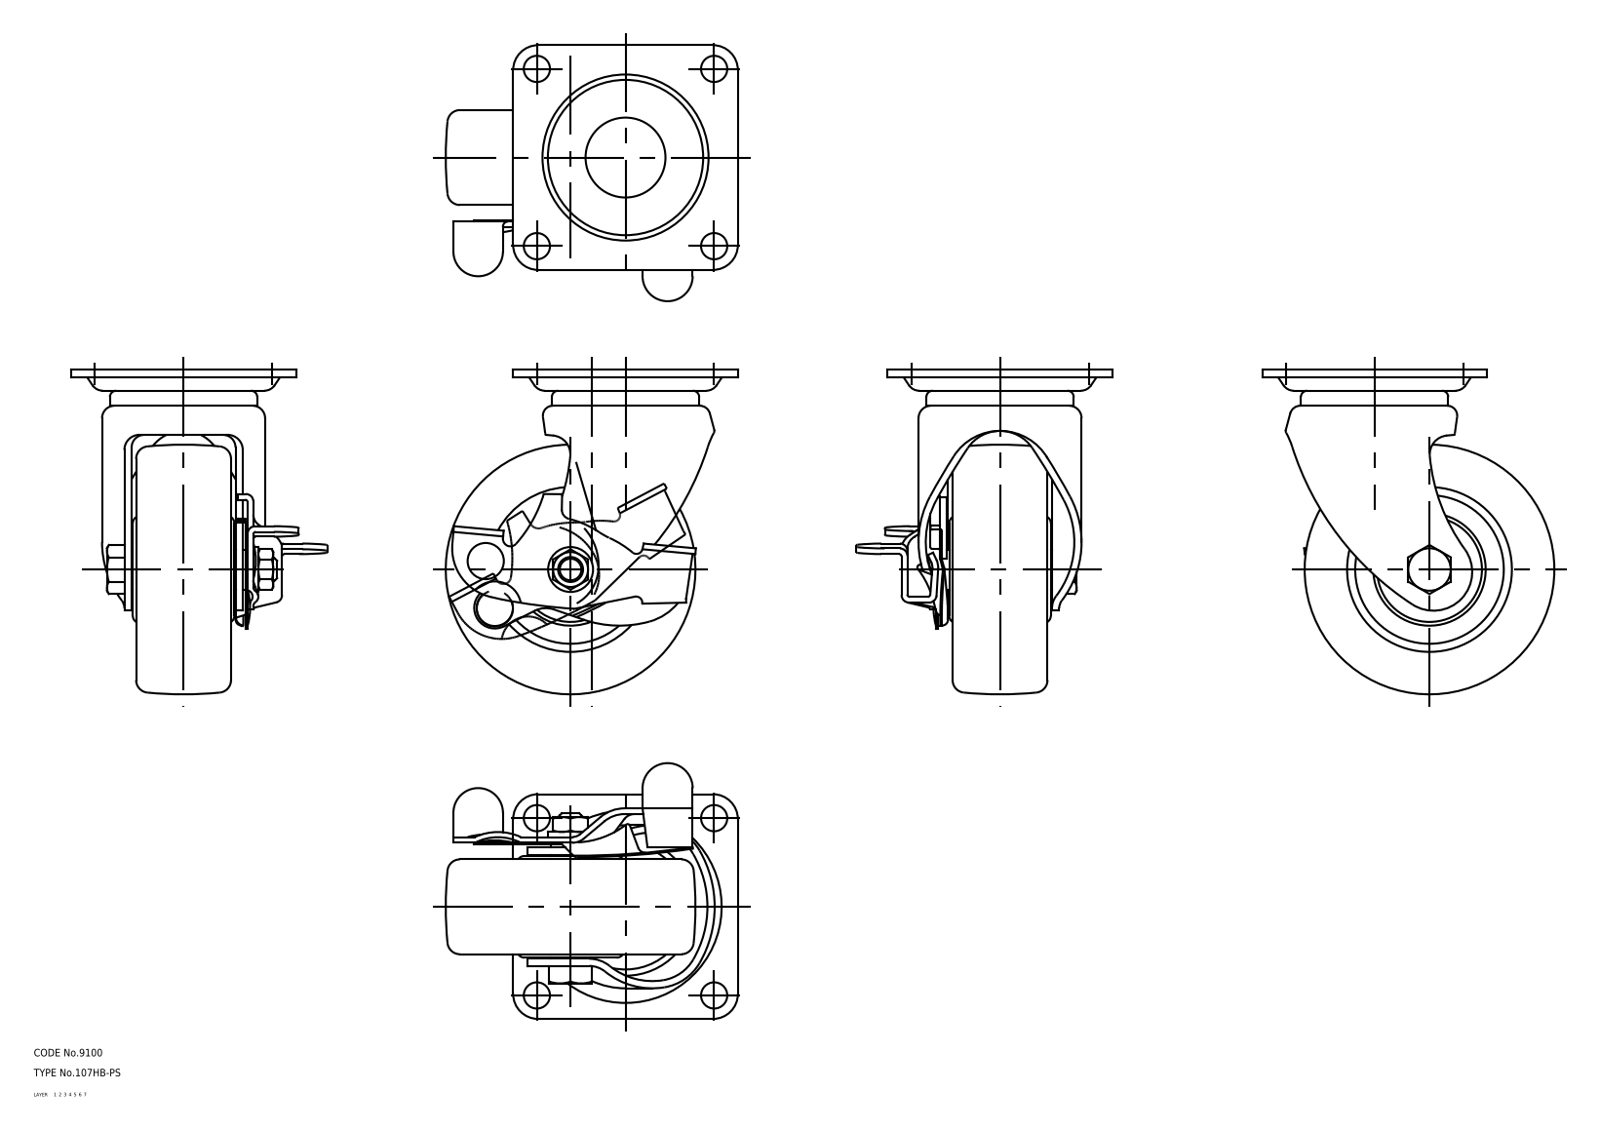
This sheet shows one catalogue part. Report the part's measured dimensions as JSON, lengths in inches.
{"part_name": "67133524; 67133537; 67133550; 67133563 (+3 more)", "step_written_by": "CADfix (AUTOMOTIVE_DESIGN)", "units": "inches", "bodies": {"solids": 7, "faces": 403, "planar": 0, "cylindrical": 0, "other": 403}, "overall_size": [5.118, 4.606, 4.037], "volume_in3": 23.62, "surface_area_in2": 151.1}
